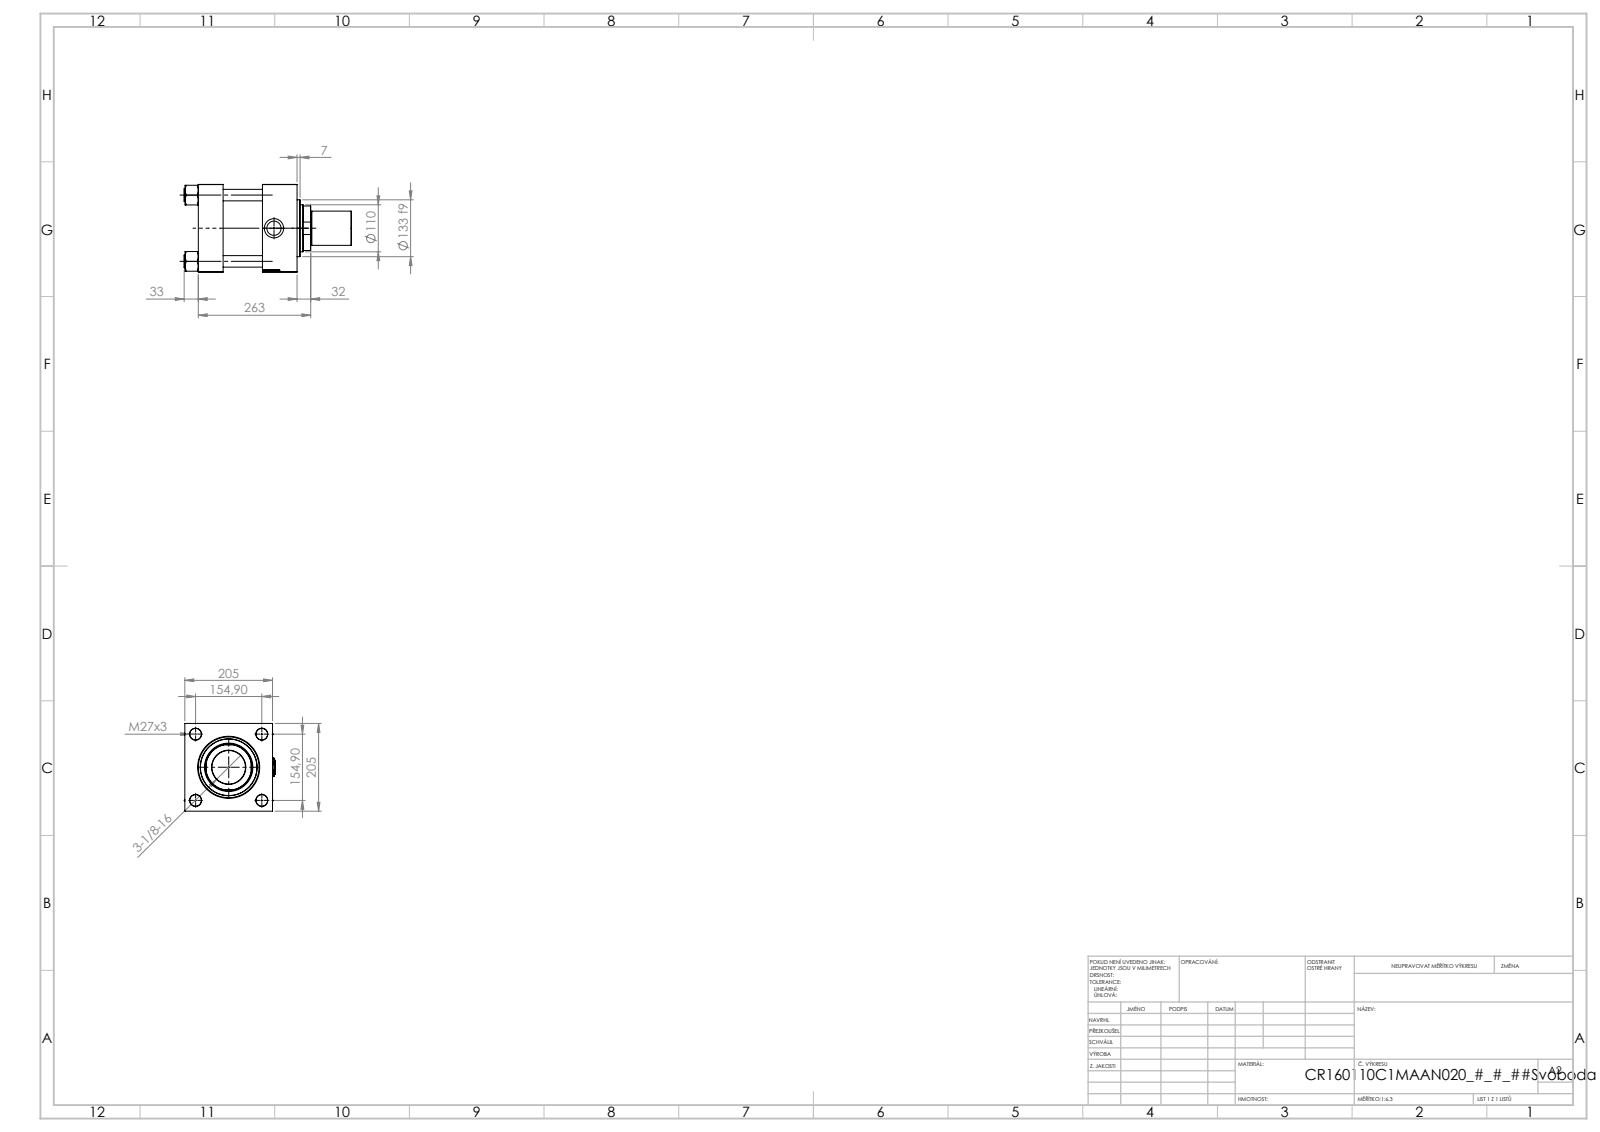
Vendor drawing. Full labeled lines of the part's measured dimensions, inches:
Part name (STEP PRODUCT): V215_VC_A; Zatka_pro_OIL_PORT; NUT_M5_C; V215CR_C_TYCINKA (+3 more)
STEP written by: SolidWorks 2019 (CONFIG_CONTROL_DESIGN)
Units: inches
Bodies: 13 solids, 1258 faces (601 planar, 95 cylindrical, 562 other)
Overall size (bounding box): 15.394 × 8.408 × 8.071
Volume: 494.1 in³ · Surface area: 1 179 in²
Round holes (diameter × count): ⌀1.063 ×4, ⌀0.276 ×2, ⌀1.309 ×2, ⌀1.772 ×2, ⌀3.091 ×1, ⌀4.331 ×1, ⌀4.449 ×1, ⌀4.724 ×1, ⌀5.591 ×1, ⌀6.299 ×1
Round bosses / shafts (diameter × count): ⌀1.181 ×4, ⌀6.535 ×1, ⌀5.236 ×1, ⌀3.15 ×1, ⌀3.071 ×1
Partial cylindrical surfaces — rounded edges, fillets, slot ends (radius × count): R2.126 ×1
Main face-to-face distances: 8.071, 2.283, 3.622, 5.906, 9.094, 6.811, 3.189, 7.965, 5.681, 2.059
Hole centre spacings: 4.312, 6.098, 8.624
